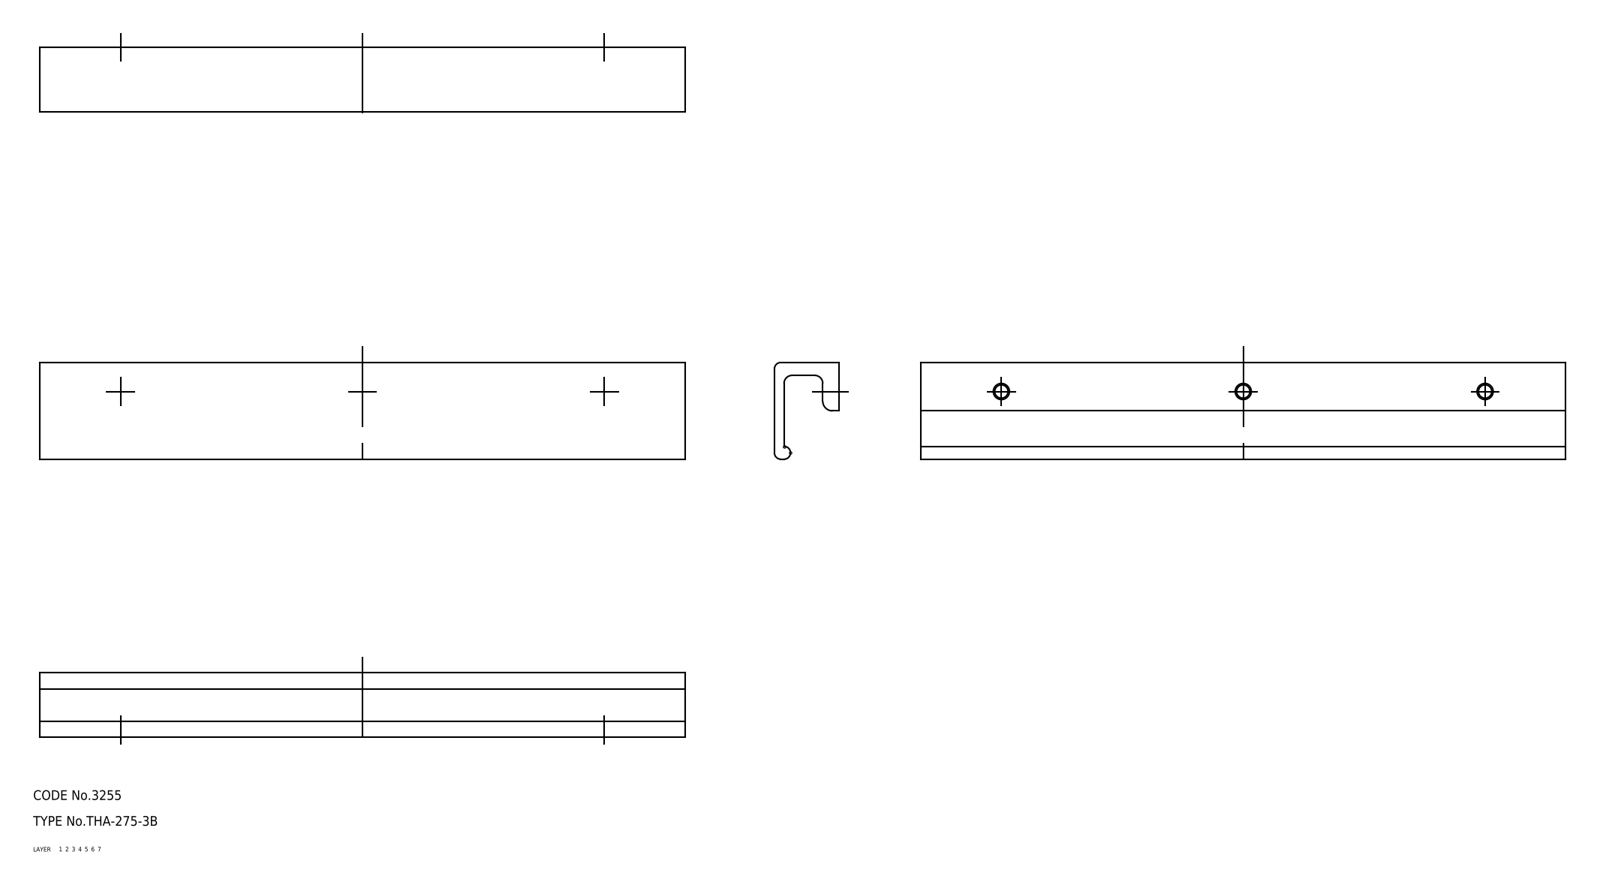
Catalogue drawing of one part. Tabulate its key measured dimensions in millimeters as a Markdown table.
| quantity | value |
| --- | --- |
| part name | pull |
| STEP written by | CADfix (AUTOMOTIVE_DESIGN) |
| units | millimeters |
| bodies | 1 solid, 22 faces (0 planar, 0 cylindrical, 22 other) |
| overall size | 200 × 30 × 20 |
| volume | 43 368 mm³ |
| surface area | 24 381 mm² |
